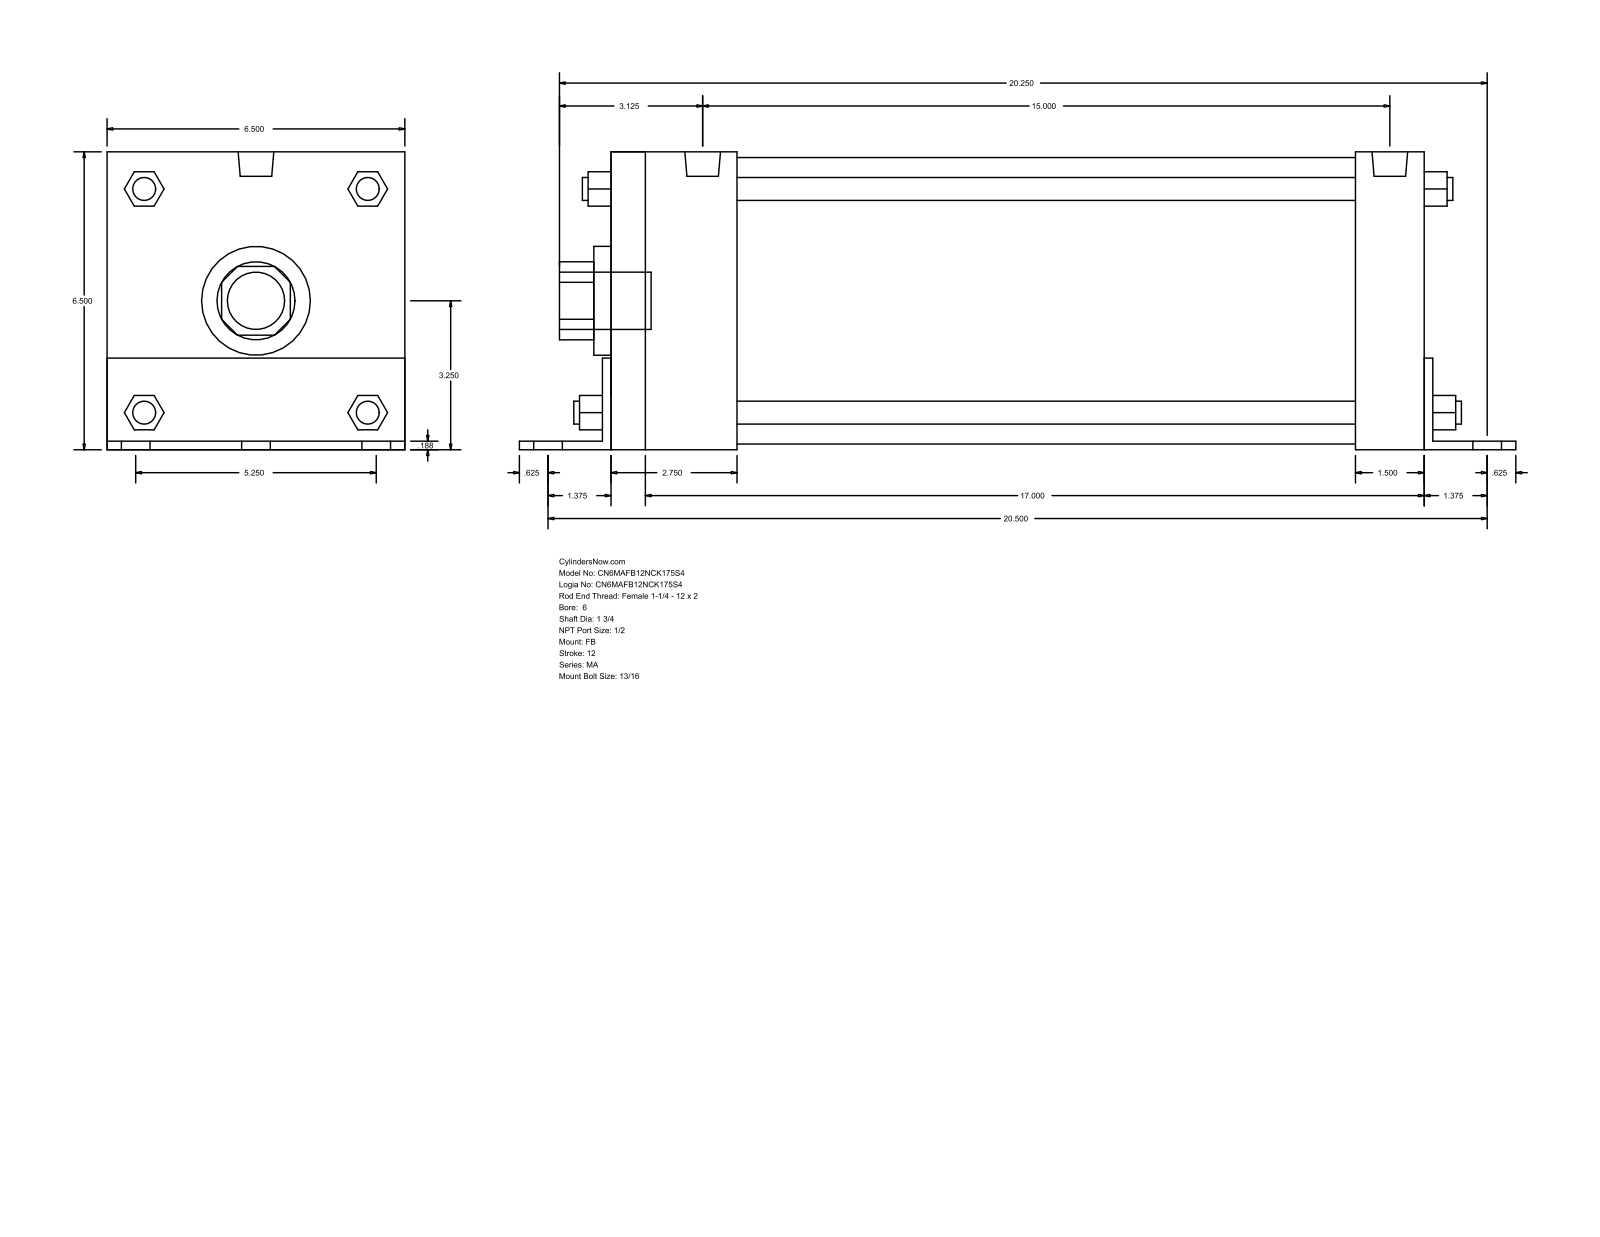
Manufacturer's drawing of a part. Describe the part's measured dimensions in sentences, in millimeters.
The part is named "MA_FB__0600_1.75". Its 3-D file was written by "GSSL Pune (CONFIG_CONTROL_DESIGN)". It is 0 solids with 140 faces: 105 planar, 35 cylindrical and 0 other. Overall it measures 552.45 by 165.15 by 165.1 millimeters. Round holes: 1 of diameter 44.45, 1 of diameter 60.33, 1 of diameter 158.75. Round bosses or shafts: 6 of diameter 20.64, 4 of diameter 17.46, 4 of diameter 12.7, 2 of diameter 19.77, 1 of diameter 31.75. Partial cylindrical surfaces (rounded edges, fillets, slot ends): 1 of radius 21.63, 1 of radius 32.05. The main face-to-face distances are 165.1, 4.76, 450.86, 165.15, 455.62, 4.71, 160.39, 460.38, 38.11, 74.61.
